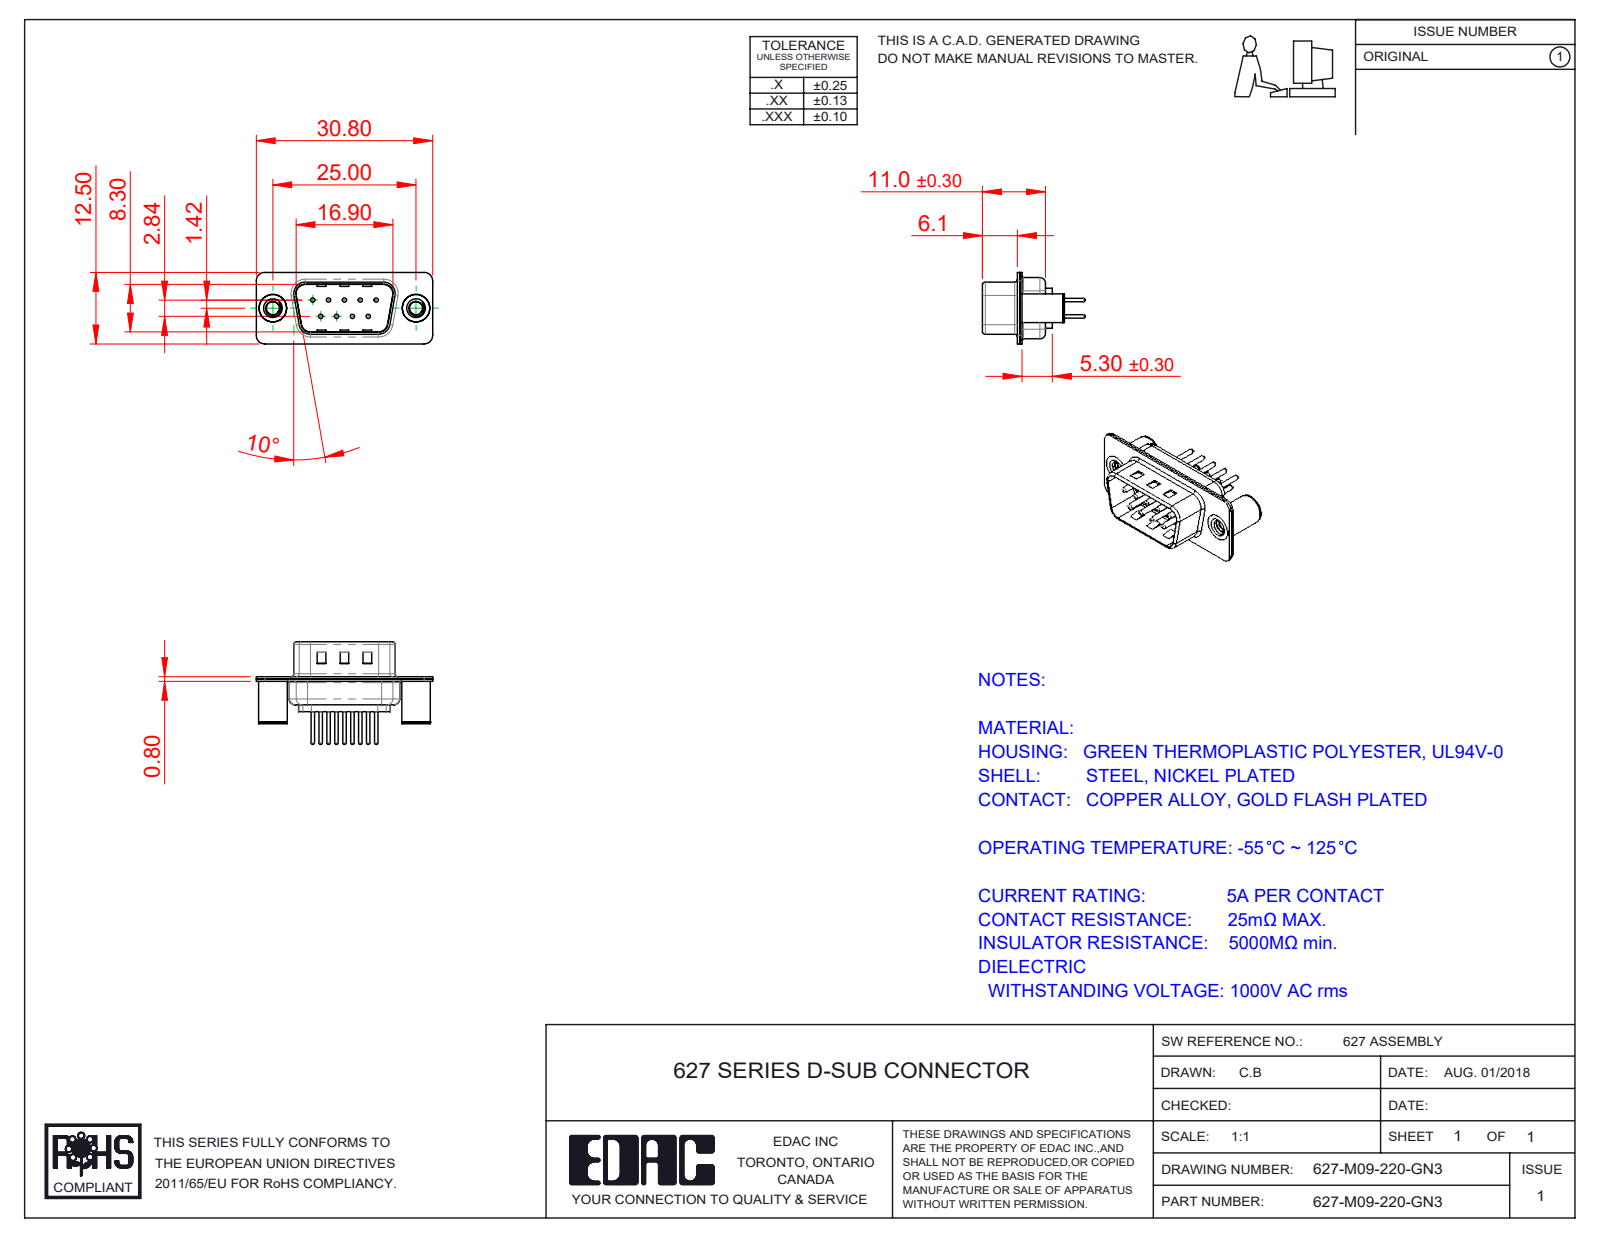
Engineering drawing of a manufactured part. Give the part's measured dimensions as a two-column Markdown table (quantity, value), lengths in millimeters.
| quantity | value |
| --- | --- |
| part name | 627M Housing_09 Contacts; 627-M09-220-GN3; 627M 4-40 Threaded Board Spacer; 627M Shell Front_09 Contacts (+3 more) |
| STEP written by | SolidWorks 2020 (CONFIG_CONTROL_DESIGN) |
| units | millimeters |
| bodies | 14 solids, 671 faces (170 planar, 279 cylindrical, 222 other) |
| overall size | 30.8 × 17.9 × 12.5 |
| volume | 1 433 mm³ |
| surface area | 3 832 mm² |
| round holes (diameter × count) | 0.75 × 9, 1.6 × 9, 2 × 9, 2.26 × 2, 3.26 × 2, 4 × 2, 4.8 × 2 |
| round bosses / shafts (diameter × count) | 1.5 × 9, 0.6 × 9, 5 × 2, 4.9 × 2 |
| partial cylindrical surfaces (radius × count) | 1.5 × 16, 2 × 12, 0.5 × 8, 1.6 × 8, 0.25 × 4, 0.6 × 4, 0.65 × 4, 0.9 × 4 |
| main face-to-face distances | 0.4, 0.8, 9.5, 9.1, 8.7, 0.65, 9.9, 1.2, 5.3, 6.1 |
| hole center spacings | 3.16, 2.77, 5.54, 5.03, 5.04, 8.31, 7.1, 7.48 |
